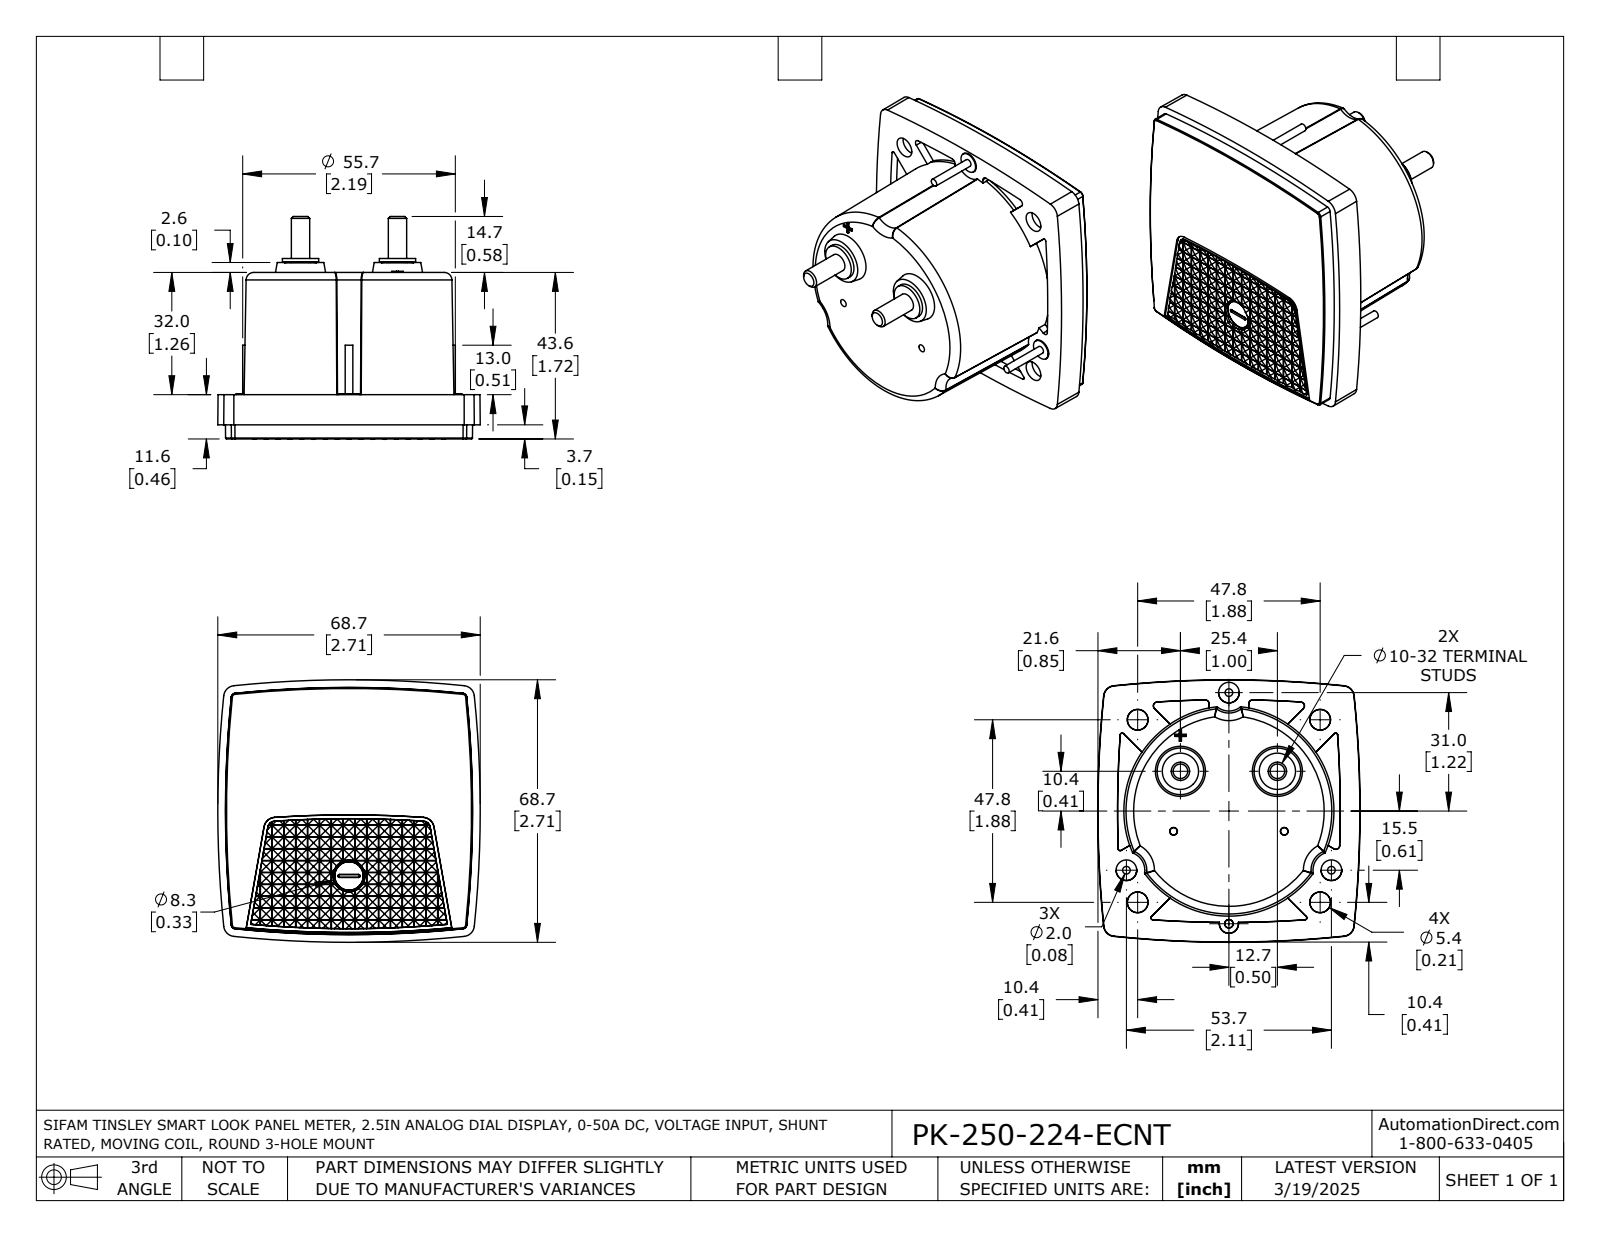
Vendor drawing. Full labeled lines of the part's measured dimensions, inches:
Part name (STEP PRODUCT): PK-250-224-ECNT
STEP written by: SolidWorks 2021 (AUTOMOTIVE_DESIGN)
Units: inches
Bodies: 1 solid, 1550 faces (1165 planar, 265 cylindrical, 120 other)
Overall size (bounding box): 2.706 × 2.706 × 2.297
Volume: 7.594 in³ · Surface area: 30.41 in²
Round bosses / shafts (diameter × count): ⌀0.213 ×3, ⌀0.079 ×3, ⌀0.374 ×2, ⌀0.189 ×2, ⌀0.215 ×1
Partial cylindrical surfaces — rounded edges, fillets, slot ends (radius × count): R0.167 ×2, R1.083 ×1
Main face-to-face distances: 1.717, 1.26, 0.457, 0.024, 0.087, 0.096, 0.311, 0.12, 0.072, 1.346
